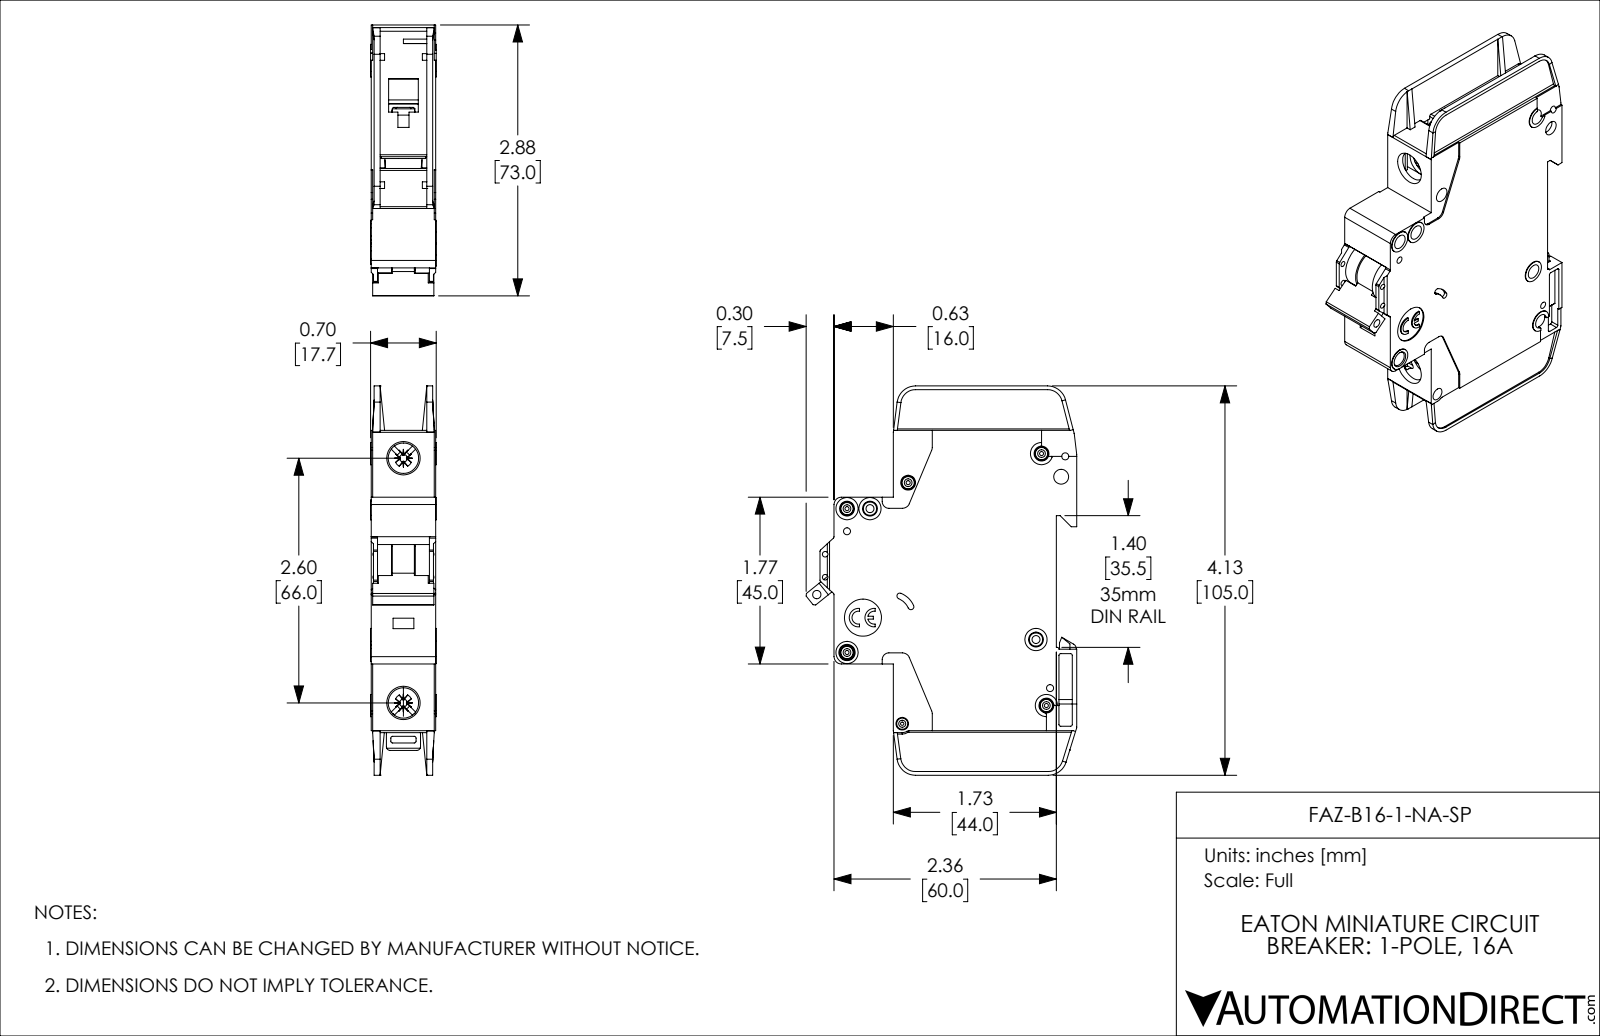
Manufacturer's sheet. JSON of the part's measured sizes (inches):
{"part_name": "FAZ-B16-1-NA-SP", "step_written_by": "SolidWorks 2019 (AUTOMOTIVE_DESIGN)", "units": "inches", "bodies": {"solids": 1, "faces": 1127, "planar": 671, "cylindrical": 357, "other": 99}, "overall_size": [4.134, 2.876, 0.697], "volume_in3": 4.682, "surface_area_in2": 41.01, "round_holes": [[0.157, 8], [0.043, 5], [0.075, 4], [0.059, 2], [0.085, 2], [0.323, 2], [0.035, 1], [0.089, 1], [0.098, 1], [0.134, 1], [0.394, 1]], "round_bosses_or_shafts": [[0.13, 5], [0.236, 4], [0.118, 2], [0.098, 1]], "partial_cylinders_radius": [[0.02, 42], [0.016, 10], [0.039, 10], [0.079, 8], [0.197, 5], [0.008, 4], [0.026, 4], [0.043, 4]], "face_to_face_distances": [0.047, 0.685, 0.591, 0.638, 0.094, 0.543, 0.016, 0.031, 0.496, 0.575], "hole_center_spacings": [0.244, 0.537, 0.87, 0.189, 0.199, 0.204, 0.221, 0.24]}
